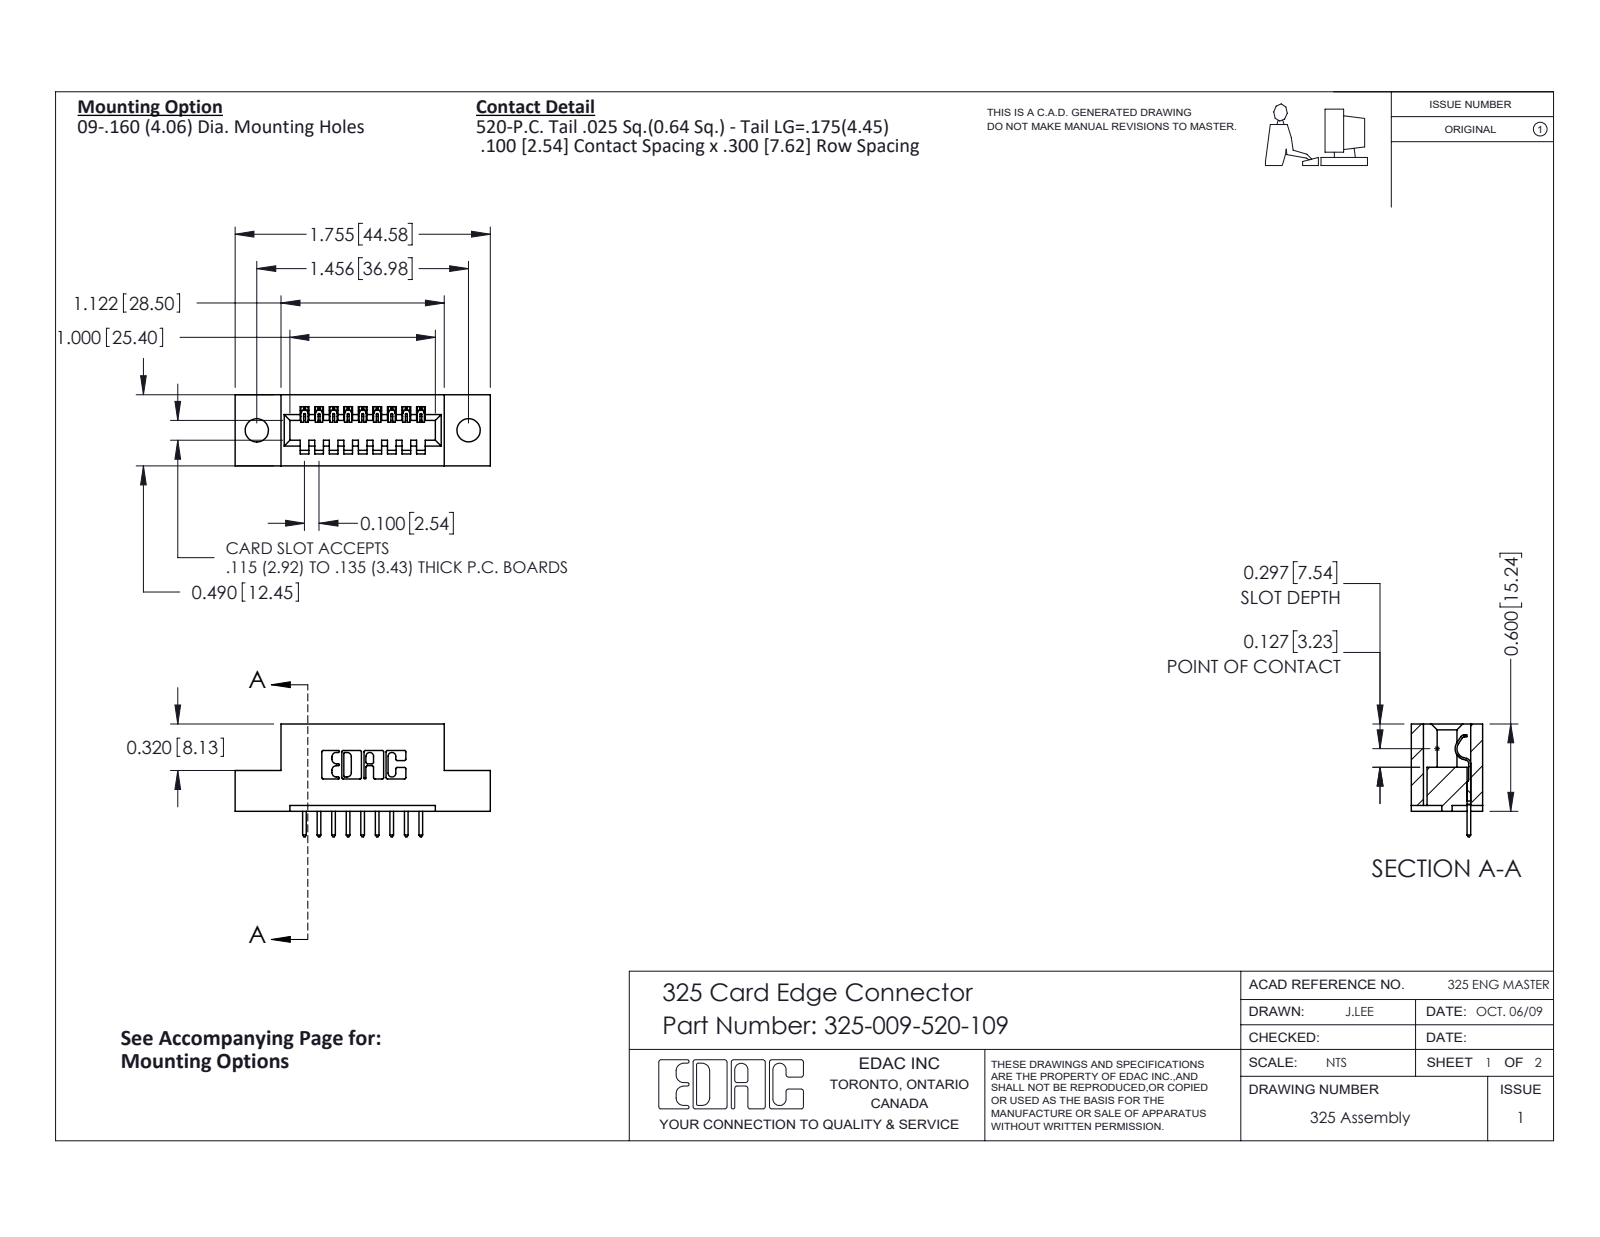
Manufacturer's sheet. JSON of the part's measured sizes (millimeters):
{"part_name": "325-009-520-109; 325 Part_.160 TH; 325-292-001_325-293-120", "step_written_by": "SolidWorks 2016 (CONFIG_CONTROL_DESIGN)", "units": "millimeters", "bodies": {"solids": 10, "faces": 636, "planar": 448, "cylindrical": 188, "other": 0}, "overall_size": [44.6, 19.7, 12.4], "volume_mm3": 5150, "surface_area_mm2": 4863, "round_holes": [[4.1, 2]], "partial_cylinders_radius": [[0.3, 22], [0.2, 18], [0.3, 18], [0.2, 6], [0.8, 6], [0.7, 3], [0.4, 1], [0.6, 1]], "face_to_face_distances": [7.6, 1, 2.5, 2.1, 10.3, 12.4, 5.1, 15.2, 10.2, 1.5], "hole_center_spacings": [37]}
